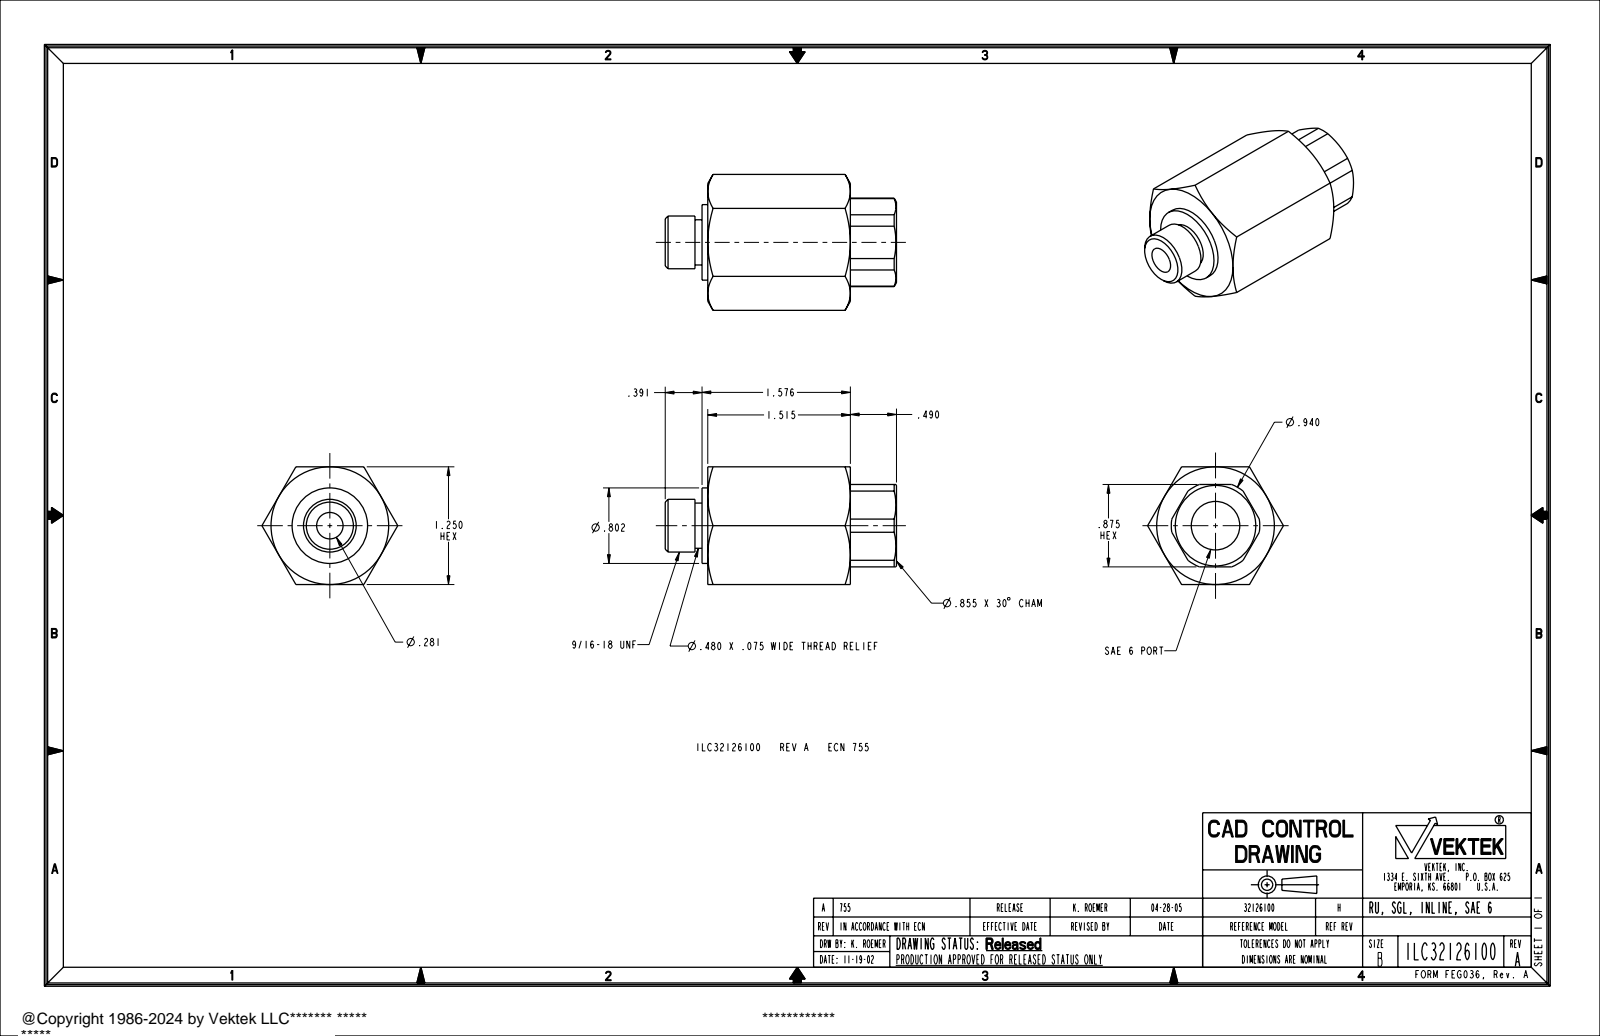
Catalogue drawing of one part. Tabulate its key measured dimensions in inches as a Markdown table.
| quantity | value |
| --- | --- |
| part name | ILC32126100 |
| STEP written by | PRO/ENGINEER BY PARAMETRIC TECHNOLOGY CORPORATION, 2004290 (AUTOMOTIVE_DESIGN_CC2) |
| units | inches |
| bodies | 1 solid, 52 faces (20 planar, 16 cylindrical, 16 other) |
| overall size | 2.457 × 1.443 × 1.25 |
| volume | 2.321 in³ |
| surface area | 13 in² |
| round holes (diameter × count) | 0.281 × 1, 0.515 × 1 |
| round bosses / shafts (diameter × count) | 0.802 × 1, 0.56 × 1, 0.48 × 1 |
| partial cylindrical surfaces (radius × count) | 0.47 × 1 |
| main face-to-face distances | 1.25, 1.25, 0.187, 1.062, 1.515, 0.875, 2.005, 0.49, 0.188, 1.063 |
